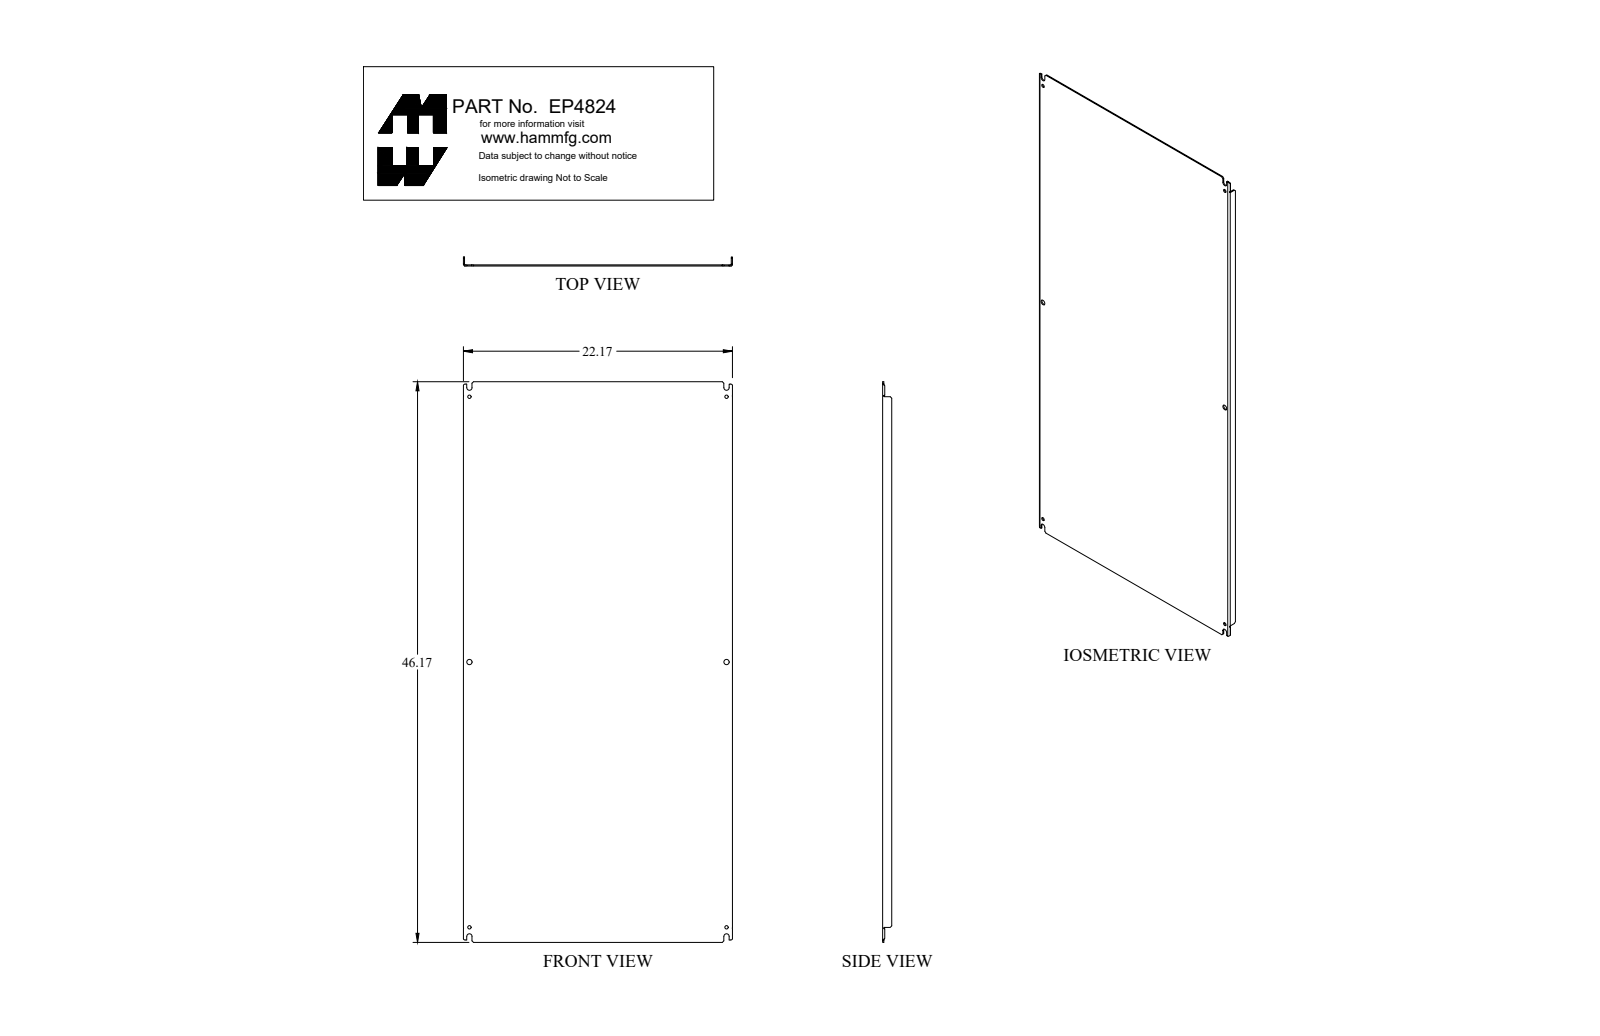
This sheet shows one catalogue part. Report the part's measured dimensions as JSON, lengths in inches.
{"part_name": "EP4824", "step_written_by": "SolidWorks 2018 (AUTOMOTIVE_DESIGN)", "units": "inches", "bodies": {"solids": 1, "faces": 88, "planar": 50, "cylindrical": 30, "other": 8}, "overall_size": [46.17, 22.17, 0.75], "volume_in3": 102.2, "surface_area_in2": 2165, "round_holes": [[0.281, 4], [0.437, 2]], "partial_cylinders_radius": [[0.219, 4], [0.048, 2], [0.063, 2], [0.143, 2]], "face_to_face_distances": [0.095, 22.075, 21.98, 22.17, 0.75, 0.655, 46.17, 0.171, 0.076, 0.579], "hole_center_spacings": [21.844, 30.432, 21.188, 43.688, 48.555]}
